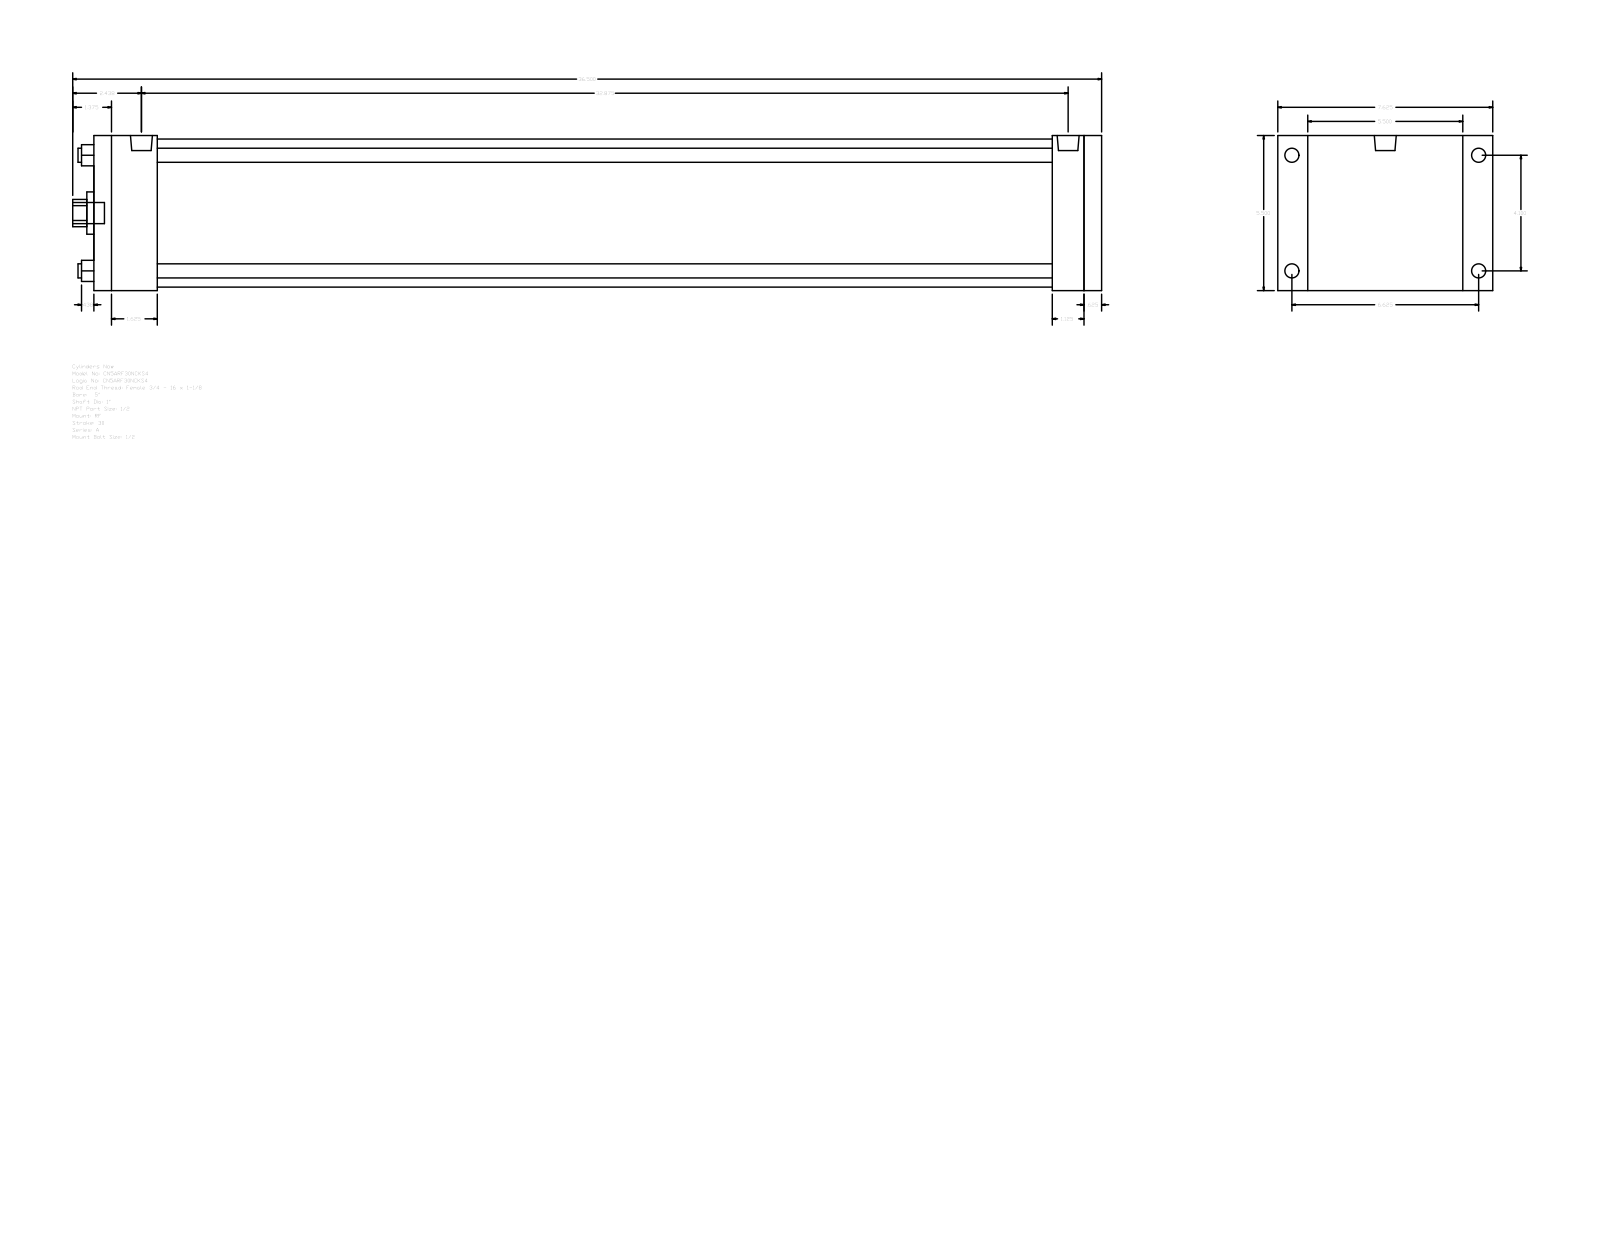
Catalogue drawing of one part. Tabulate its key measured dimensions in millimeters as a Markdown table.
| quantity | value |
| --- | --- |
| part name | A_RF__0500_1 |
| STEP written by | GSSL Pune (CONFIG_CONTROL_DESIGN) |
| units | millimeters |
| bodies | 0 solids, 92 faces (64 planar, 28 cylindrical, 0 other) |
| overall size | 927.1 × 193.68 × 139.7 |
| round holes (diameter × count) | 12.7 × 4, 25.4 × 1, 38.1 × 1, 133.35 × 1 |
| round bosses / shafts (diameter × count) | 12.7 × 4, 8.73 × 4, 19.77 × 2, 19.05 × 1 |
| partial cylindrical surfaces (radius × count) | 12.29 × 1 |
| main face-to-face distances | 139.7, 908.05, 15.87, 892.18, 57.15, 835.03, 850.9, 863.6, 806.45, 28.58 |
| hole center spacings | 73.64, 104.14, 147.28 |
